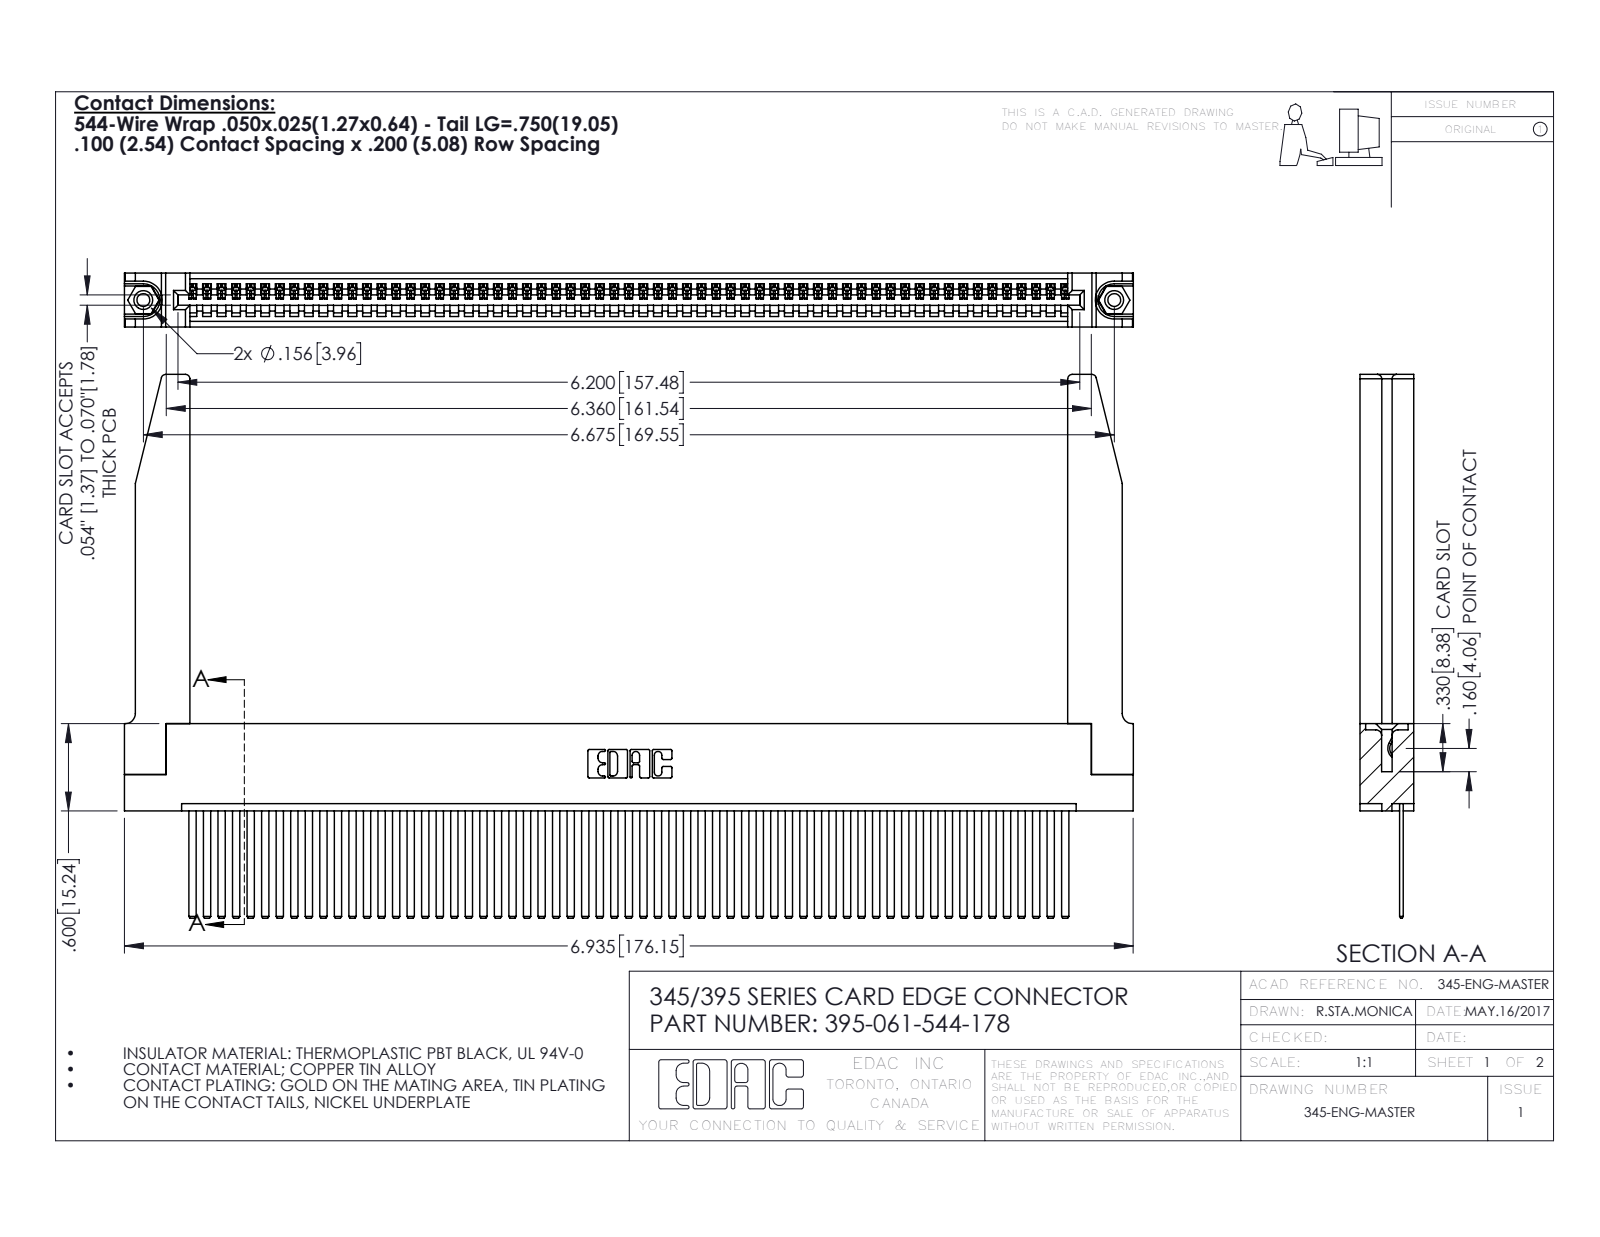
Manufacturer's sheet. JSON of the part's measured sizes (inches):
{"part_name": "345-220-078_345-220-078; 345 Part_Flush Mounting Lugs - 0.156 Dia-TH; 345-292-001_345-293-144; 345-250-001_345-250-001-102 (+1 more)", "step_written_by": "SolidWorks 2016 (CONFIG_CONTROL_DESIGN)", "units": "inches", "bodies": {"solids": 66, "faces": 3532, "planar": 2418, "cylindrical": 1062, "other": 52}, "overall_size": [6.936, 3.737, 0.37], "volume_in3": 1.548, "surface_area_in2": 50.54, "round_holes": [[0.089, 2], [0.125, 2], [0.156, 2], [0.064, 1]], "round_bosses_or_shafts": [[0.155, 2]], "partial_cylinders_radius": [[0.006, 122], [0.01, 22], [0.03, 8], [0.007, 6], [0.031, 6], [0.026, 3], [0.031, 2], [0.04, 2]], "face_to_face_distances": [0.072, 0.298, 0.37, 0.098, 0.272, 0.025, 0.2, 0.225, 0.148, 0.15], "hole_center_spacings": [0.27, 6.439, 6.675]}
